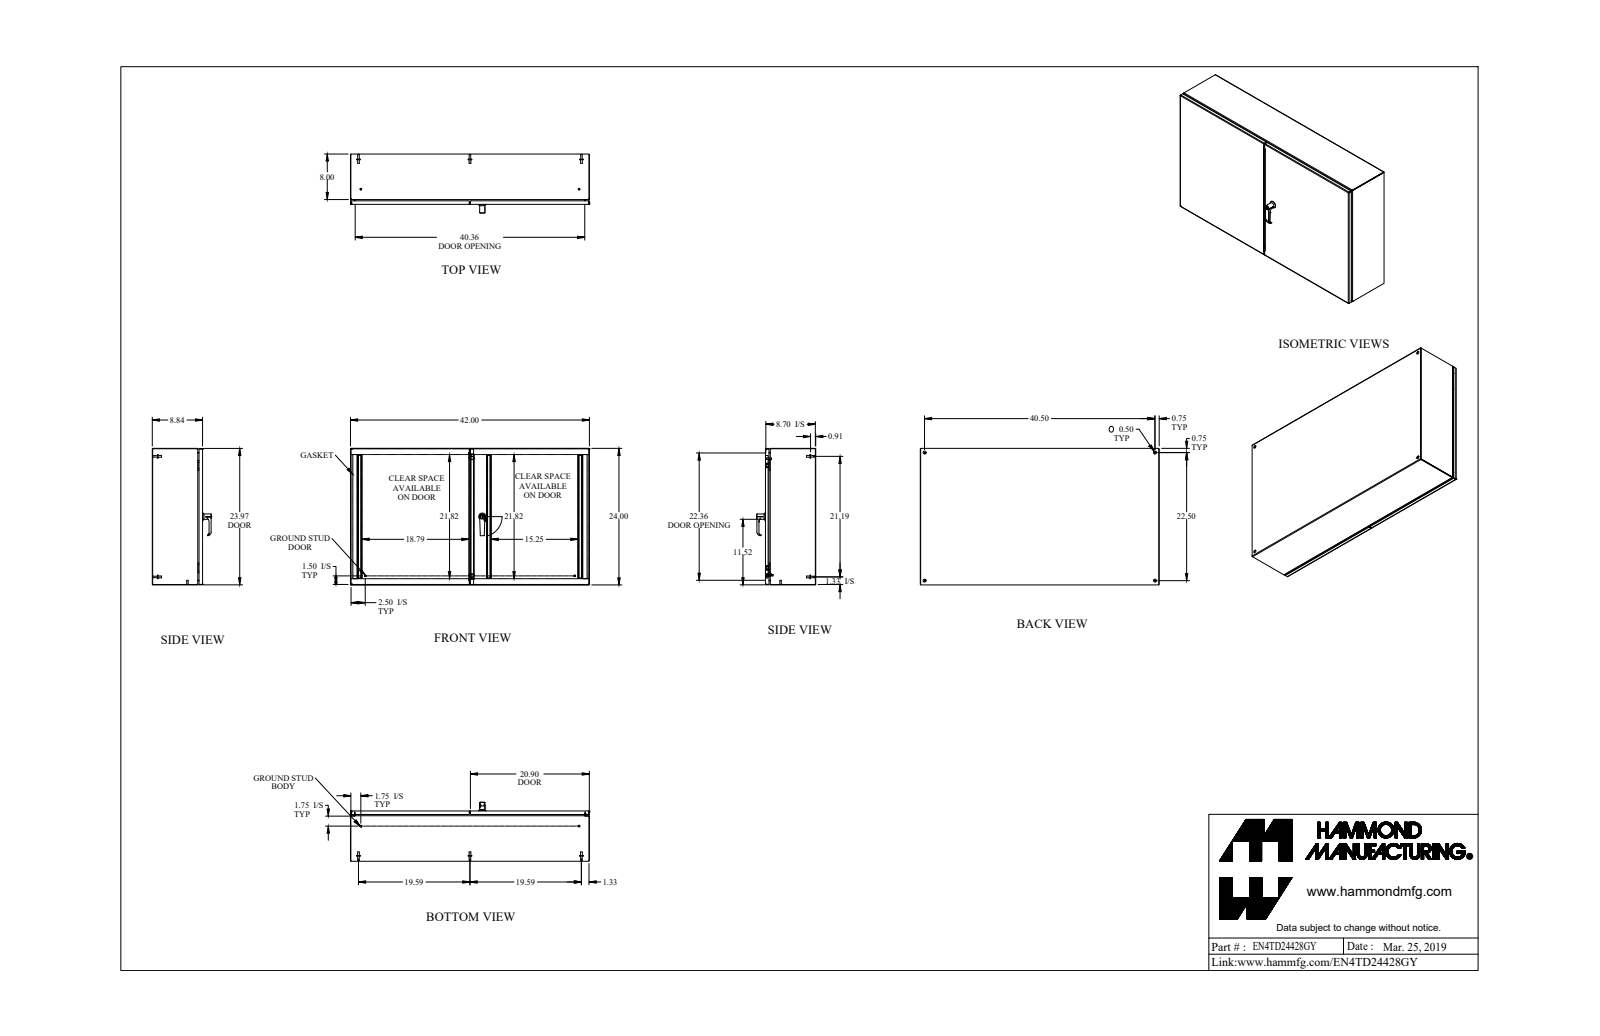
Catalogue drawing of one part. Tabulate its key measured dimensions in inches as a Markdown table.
| quantity | value |
| --- | --- |
| part name | EN4TD24428GY |
| STEP written by | SolidWorks 2018 (AUTOMOTIVE_DESIGN) |
| units | inches |
| bodies | 78 solids, 1941 faces (885 planar, 718 cylindrical, 338 other) |
| overall size | 42 × 24 × 10.372 |
| volume | 287.9 in³ |
| surface area | 7 459 in² |
| round holes (diameter × count) | 0.196 × 5, 0.176 × 4, 0.265 × 4, 0.5 × 4, 0.24 × 3, 0.242 × 3, 0.172 × 2, 0.25 × 2, 0.256 × 2, 0.26 × 2, 0.313 × 2, 0.394 × 2 |
| round bosses / shafts (diameter × count) | 0.25 × 12, 0.313 × 8, 0.625 × 6, 0.27 × 6, 0.51 × 4, 0.281 × 4, 0.156 × 4, 0.75 × 3 |
| partial cylindrical surfaces (radius × count) | 0.036 × 26, 0.108 × 26, 0.094 × 20, 0.043 × 18, 0.062 × 18, 0.081 × 18, 0.02 × 16, 0.016 × 15 |
| main face-to-face distances | 0.072, 8.77, 8.698, 8.842, 23.928, 41.928, 23.856, 24, 41.856, 42 |
| hole center spacings | 0.787, 10.188, 21.296, 22.5, 22.756, 25.082, 40.5, 46.33 |
